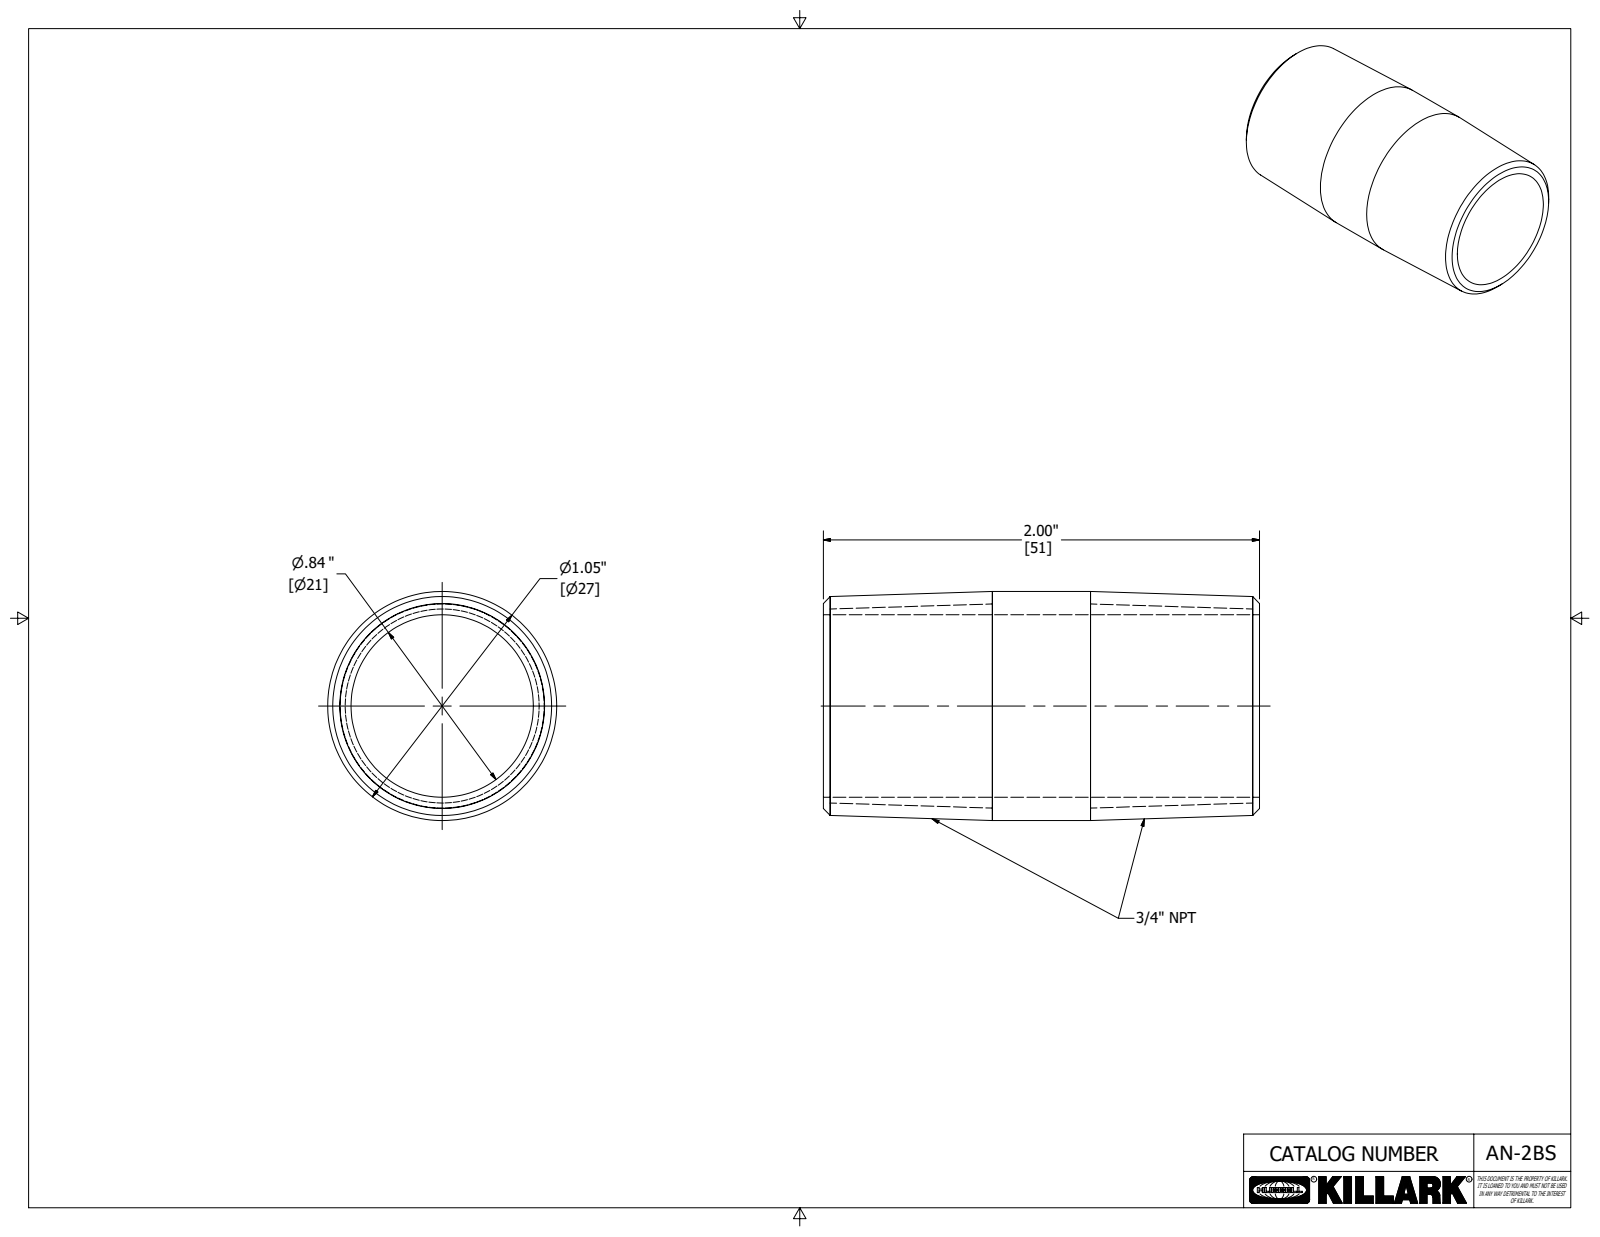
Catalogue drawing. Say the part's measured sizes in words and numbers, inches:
The part is named "14077-12". Its 3-D file was written by "Autodesk Inventor 2020 (AUTOMOTIVE_DESIGN)". It is 1 solid with 8 faces: 2 planar, 2 cylindrical and 4 other. Overall it measures 2 by 1.05 by 1.05 inches. Its volume is 0.57 cubic inches and its surface area 12.1 square inches. Round holes: 1 of diameter 0.836. Round bosses or shafts: 1 of diameter 1.05. The main face-to-face distances are 2.
